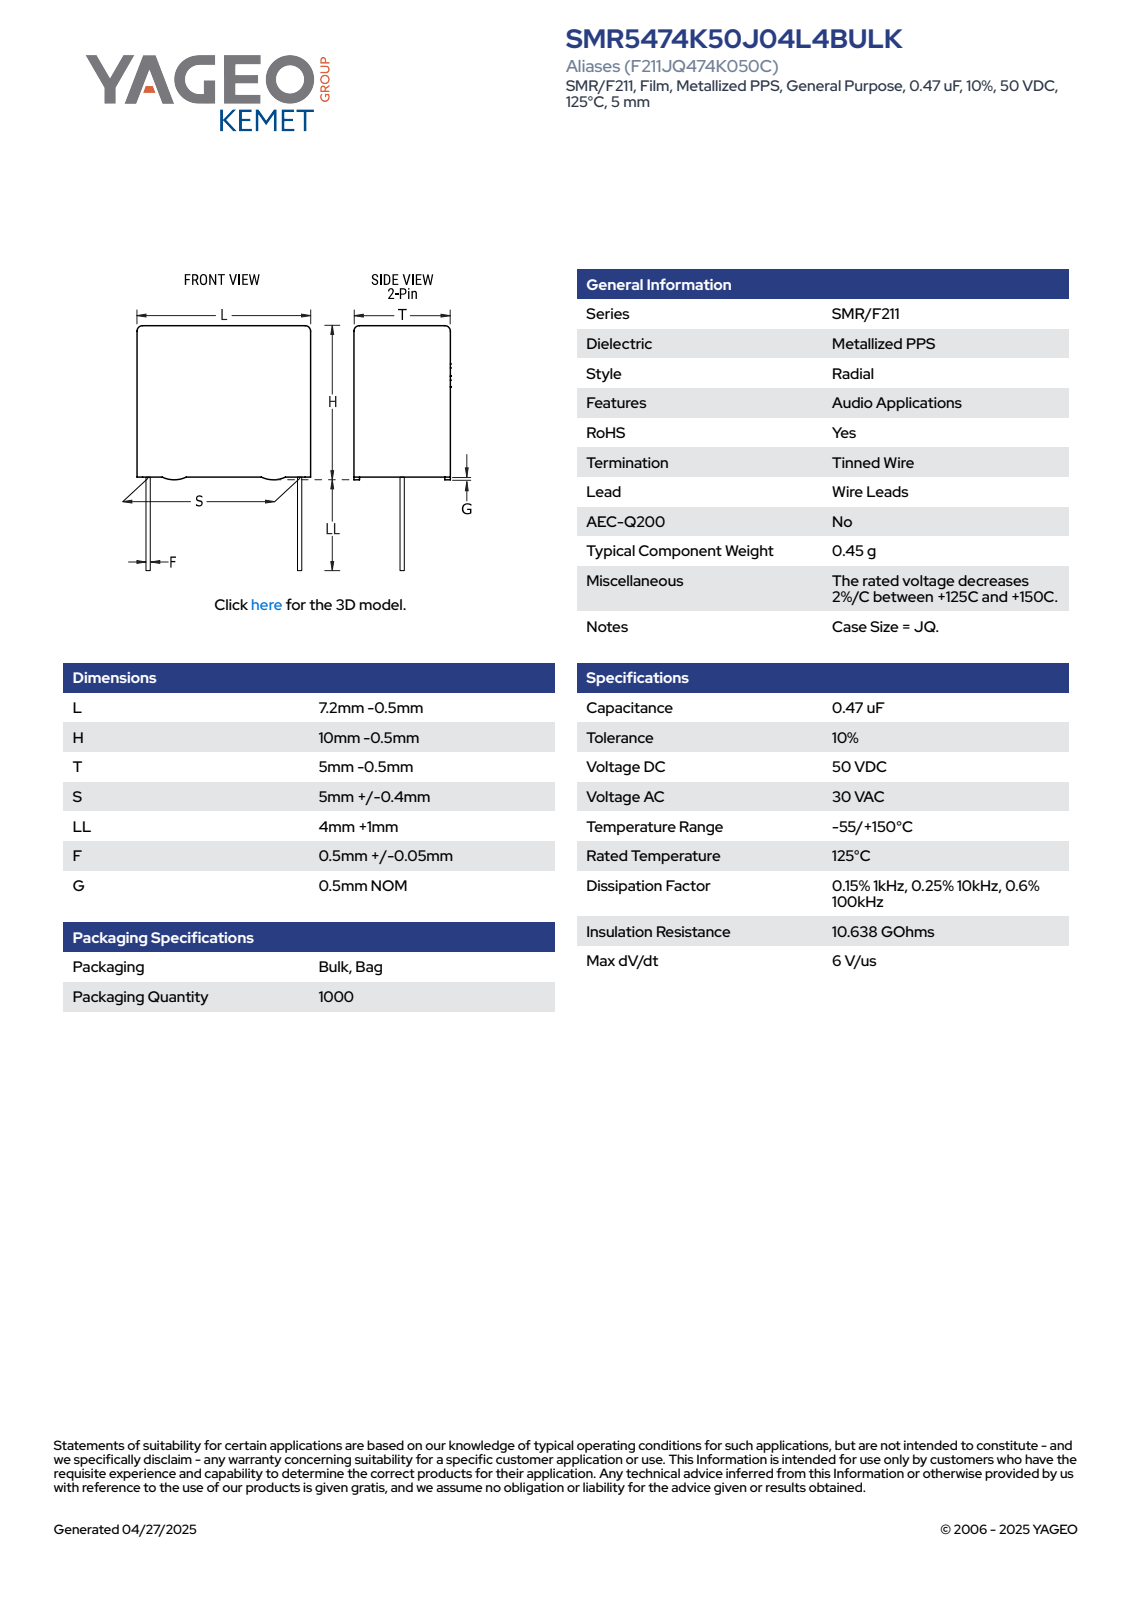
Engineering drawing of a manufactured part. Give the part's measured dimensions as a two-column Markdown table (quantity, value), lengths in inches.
| quantity | value |
| --- | --- |
| part name | CFR_RBG_7.2X10X5_L6.7H9.5T4.5S5LL5F0.55G0.5 |
| STEP written by | SolidWorks 2021 (AUTOMOTIVE_DESIGN) |
| units | inches |
| bodies | 4 solids, 89 faces (81 planar, 8 cylindrical, 0 other) |
| overall size | 0.571 × 0.264 × 0.177 |
| volume | 0.017 in³ |
| surface area | 0.443 in² |
| round bosses / shafts (diameter × count) | 0.022 × 2 |
| partial cylindrical surfaces (radius × count) | 0.02 × 4 |
| main face-to-face distances | 0.177, 0.264, 0.354, 0.167, 0.157, 0.02, 0.374, 0.098, 0.197, 0.217 |
